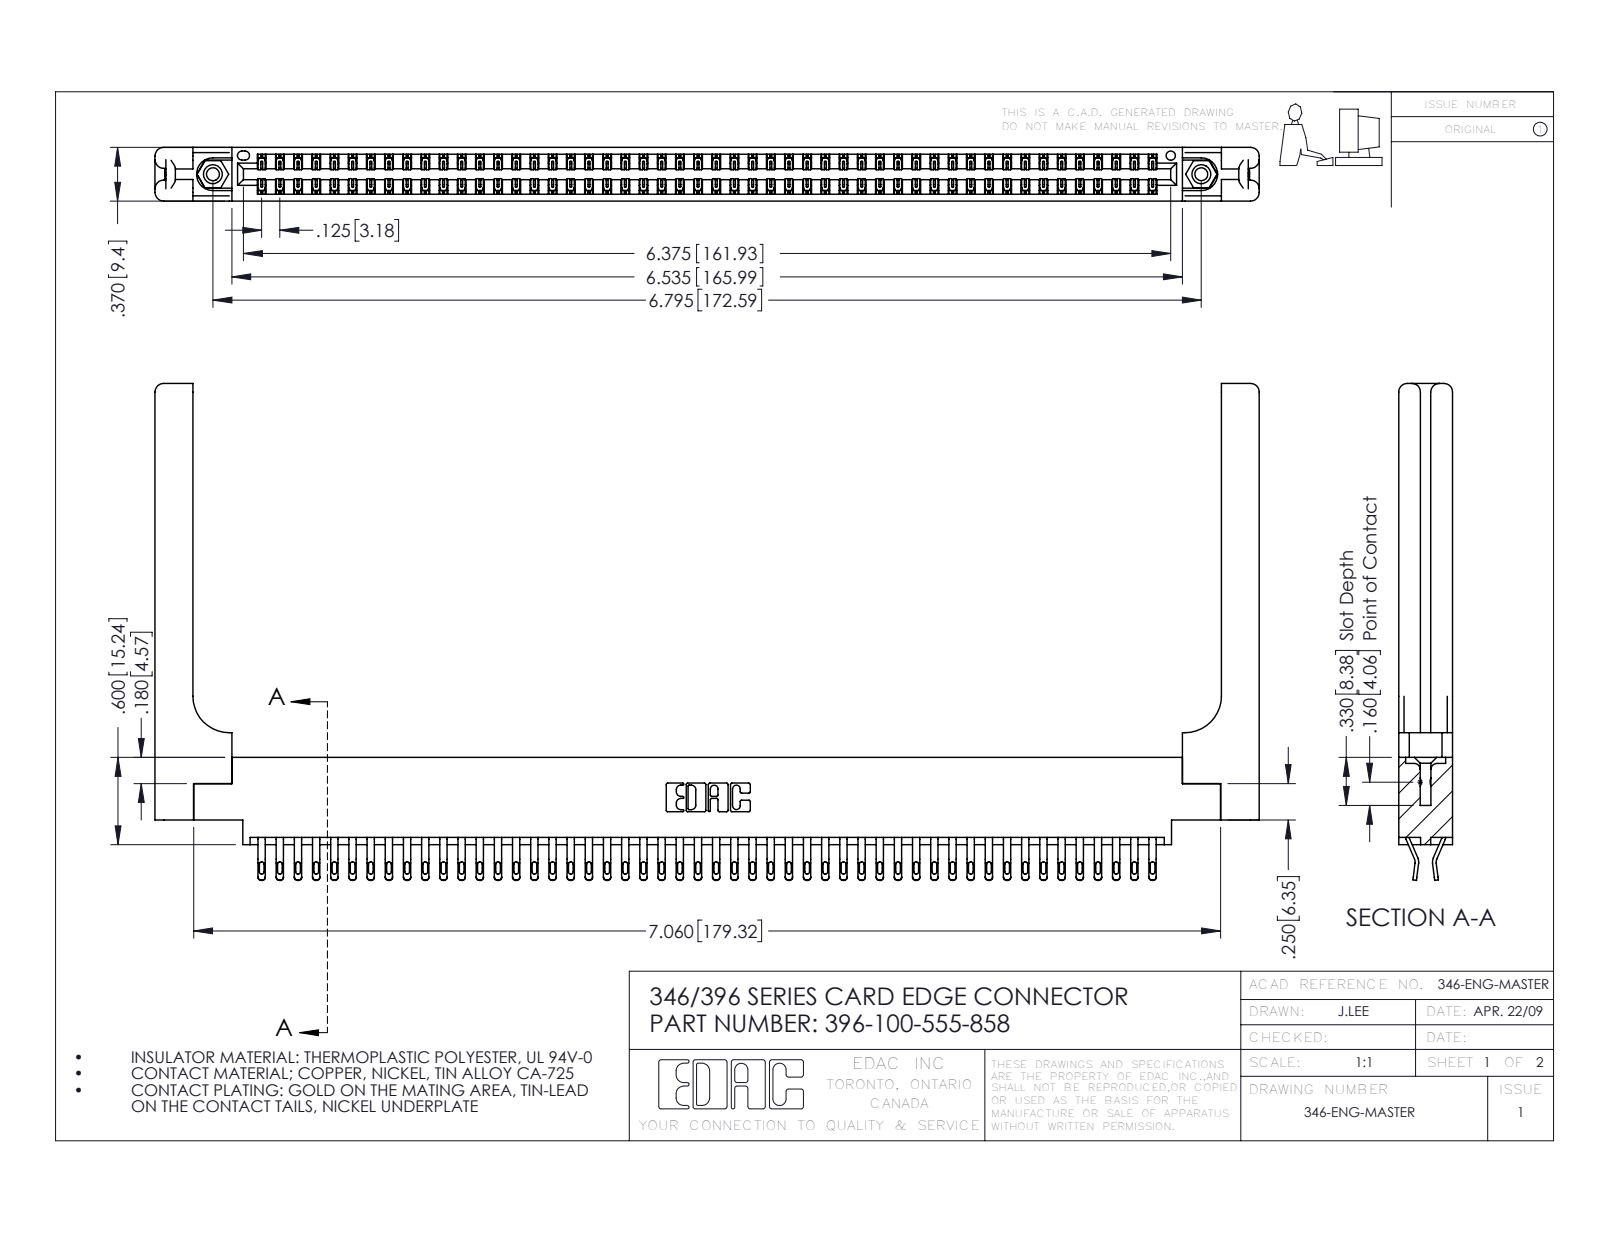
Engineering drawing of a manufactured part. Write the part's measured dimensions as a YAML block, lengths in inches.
part_name: "345-250-001_345-250-001-102; 346-220-058_345-220-058; 396-100-555-858; 346 Part_0.170 Offset - 0.156 Dia-TH (+1 more)"
step_written_by: "SolidWorks 2016 (CONFIG_CONTROL_DESIGN)"
units: inches
bodies: {solids: 105, faces: 6182, planar: 3528, cylindrical: 2594, other: 60}
overall_size: [7.591, 3.415, 0.37]
volume: 1.617
surface_area: 50.26
round_holes:
  - {diameter: 0.089, count: 2}
  - {diameter: 0.125, count: 2}
  - {diameter: 0.156, count: 2}
  - {diameter: 0.064, count: 1}
round_bosses_or_shafts:
  - {diameter: 0.155, count: 2}
partial_cylinders:
  - {radius: 0.016, count: 200}
  - {radius: 0.02, count: 200}
  - {radius: 0.006, count: 150}
  - {radius: 0.01, count: 22}
  - {radius: 0.06, count: 16}
  - {radius: 0.007, count: 6}
  - {radius: 0.031, count: 6}
  - {radius: 0.026, count: 3}
face_to_face_distances: [0.37, 0.048, 0.322, 0.072, 0.148, 0.15, 0.25, 0.025, 0.298, 0.275]
hole_center_spacings: [0.246, 6.586, 6.795]
